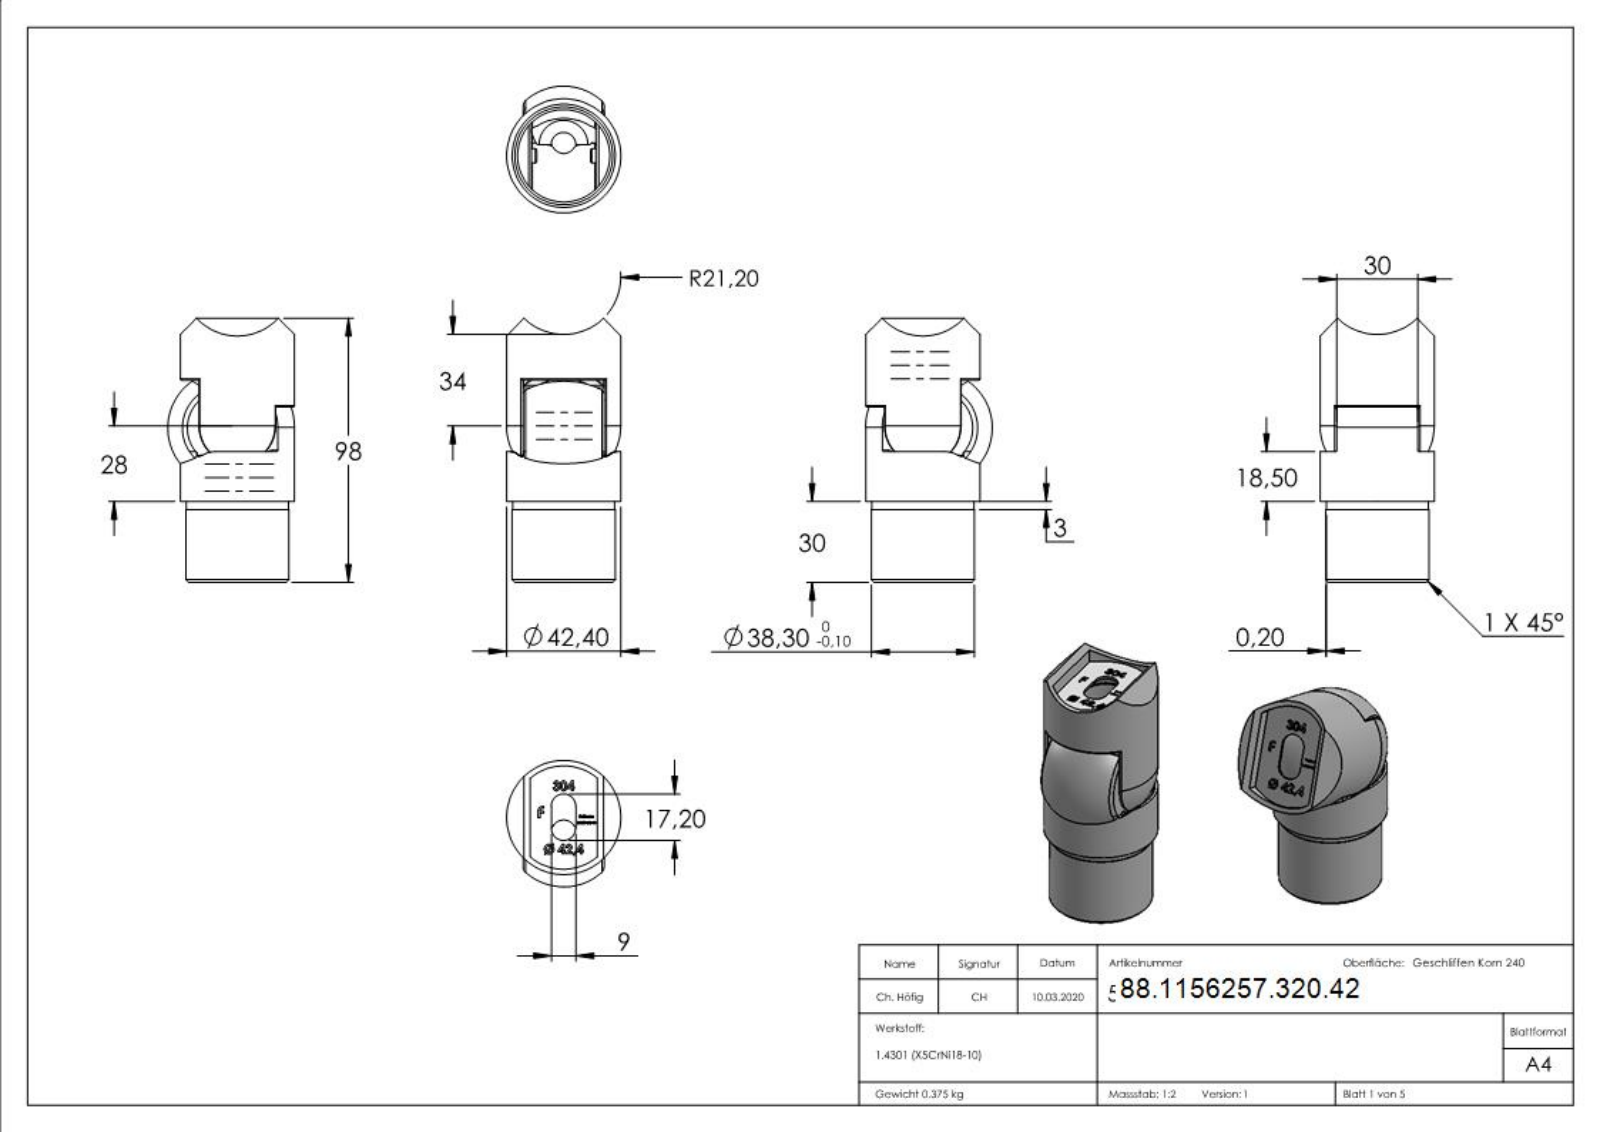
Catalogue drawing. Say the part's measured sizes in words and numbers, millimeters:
The part is named "56257-320-42 Teil2_56257-320-42 Teil2; 56257-320-42; 56257-320-42 Teil1_56257-320-42 Teil1; 56257-320-42 Teil1 (+1 more)". Its 3-D file was written by "SolidWorks 2015 (CONFIG_CONTROL_DESIGN)". It is 2 solids with 562 faces: 269 planar, 49 cylindrical and 244 other. Overall it measures 98 by 47 by 42.4 millimeters. Its volume is 47 525 cubic millimeters and its surface area 30 361 square millimeters. Round holes: 1 of diameter 6, 1 of diameter 34.3, 1 of diameter 36.4. Round bosses or shafts: 1 of diameter 42.4, 1 of diameter 38.3, 1 of diameter 37.9, 1 of diameter 5.2, 1 of diameter 3.5. Partial cylindrical surfaces (rounded edges, fillets, slot ends): 12 of radius 0.5, 8 of radius 1, 3 of radius 4.5, 2 of radius 2.5, 2 of radius 9, 1 of radius 6.75, 1 of radius 11.75, 1 of radius 14.98. The main face-to-face distances are 30, 3, 27, 24, 6, 2.5, 27.5, 0.5, 24.5, 55.
